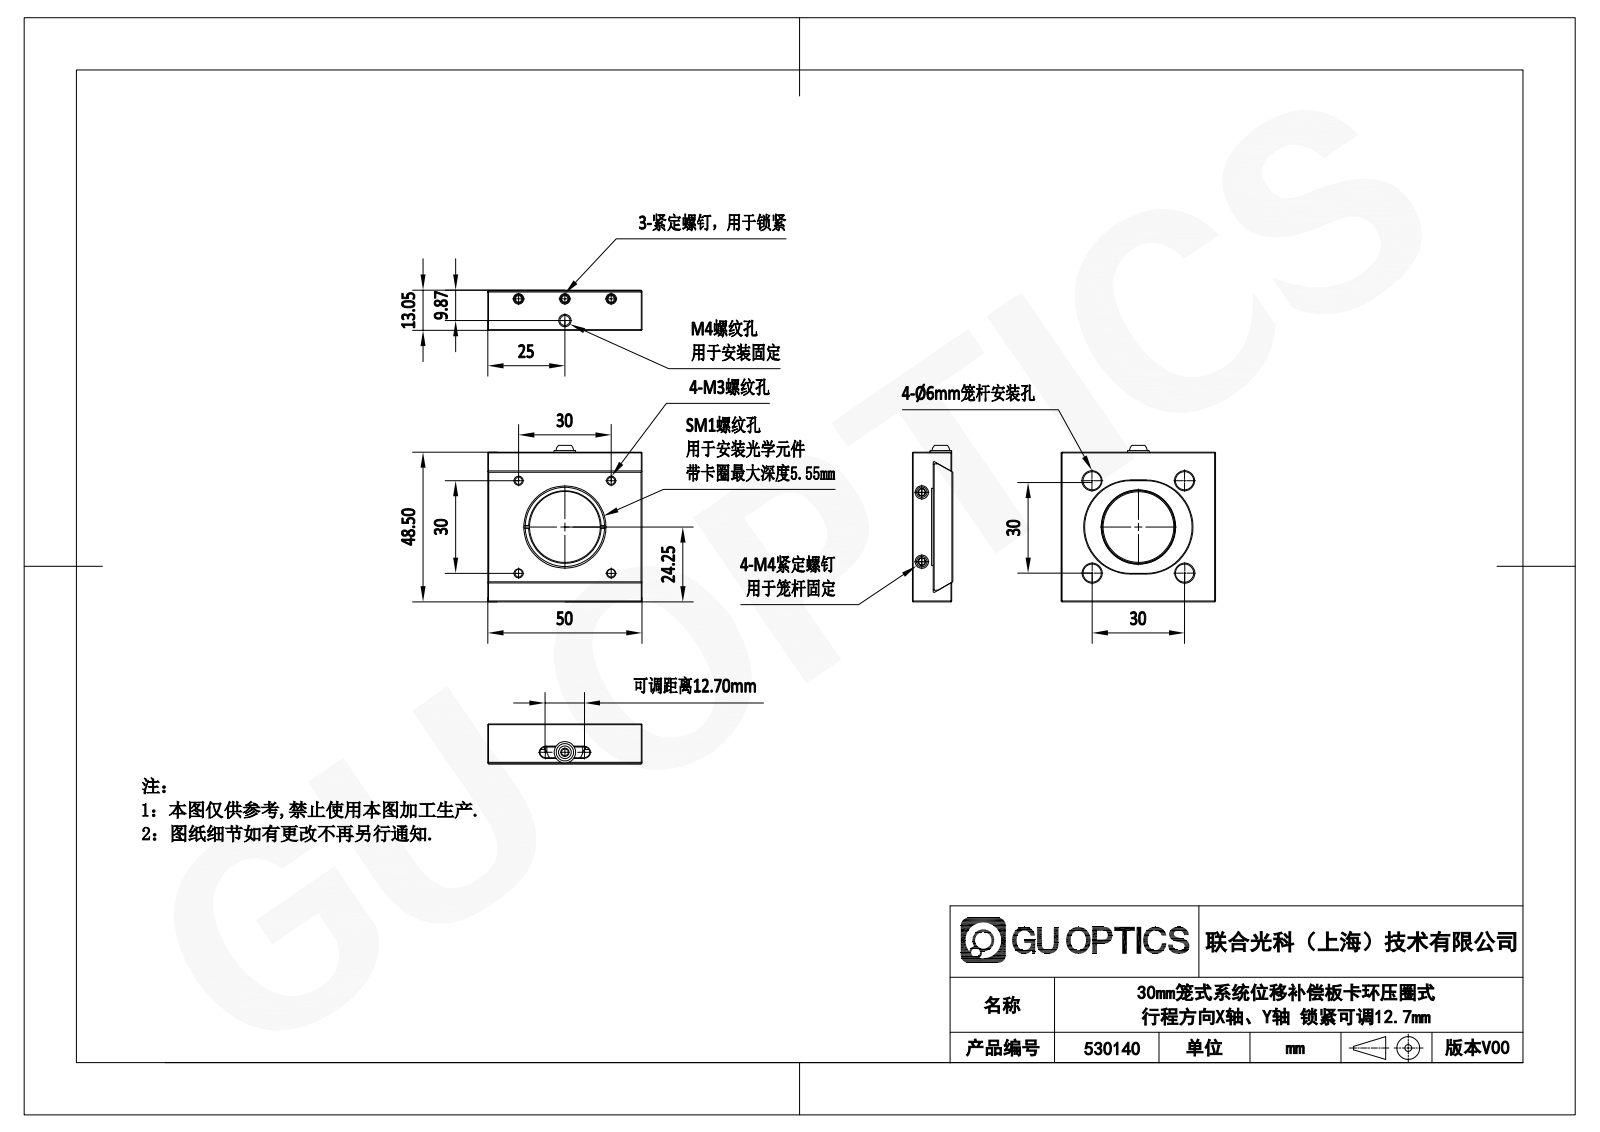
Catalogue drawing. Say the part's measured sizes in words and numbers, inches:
The part is named "530140". Its 3-D file was written by "SolidWorks 2020 (CONFIG_CONTROL_DESIGN)". It is 9 solids with 248 faces: 130 planar, 39 cylindrical and 79 other. Overall it measures 1.996 by 1.969 by 0.514 inches. Its volume is 1.292 cubic inches and its surface area 21.29 square inches. Round holes: 8 of diameter 0.098, 4 of diameter 0.236, 3 of diameter 0.13, 1 of diameter 0.126, 1 of diameter 0.902, 1 of diameter 0.947, 1 of diameter 1.01, 1 of diameter 1.049. Round bosses or shafts: 2 of diameter 0.157, 1 of diameter 1.035, 1 of diameter 0.276, 1 of diameter 0.118. Partial cylindrical surfaces (rounded edges, fillets, slot ends): 2 of radius 0.012, 2 of radius 0.039, 2 of radius 0.069, 2 of radius 0.118, 2 of radius 0.591. The main face-to-face distances are 0.264, 0.514, 0.25, 0.236, 0.5, 0.014, 1.909, 1.969, 0.02, 0.244. The hole center spacings are 1.181, 0.835, 0.591, 0.592, 0.652, 1.67, 0.039, 0.237.
